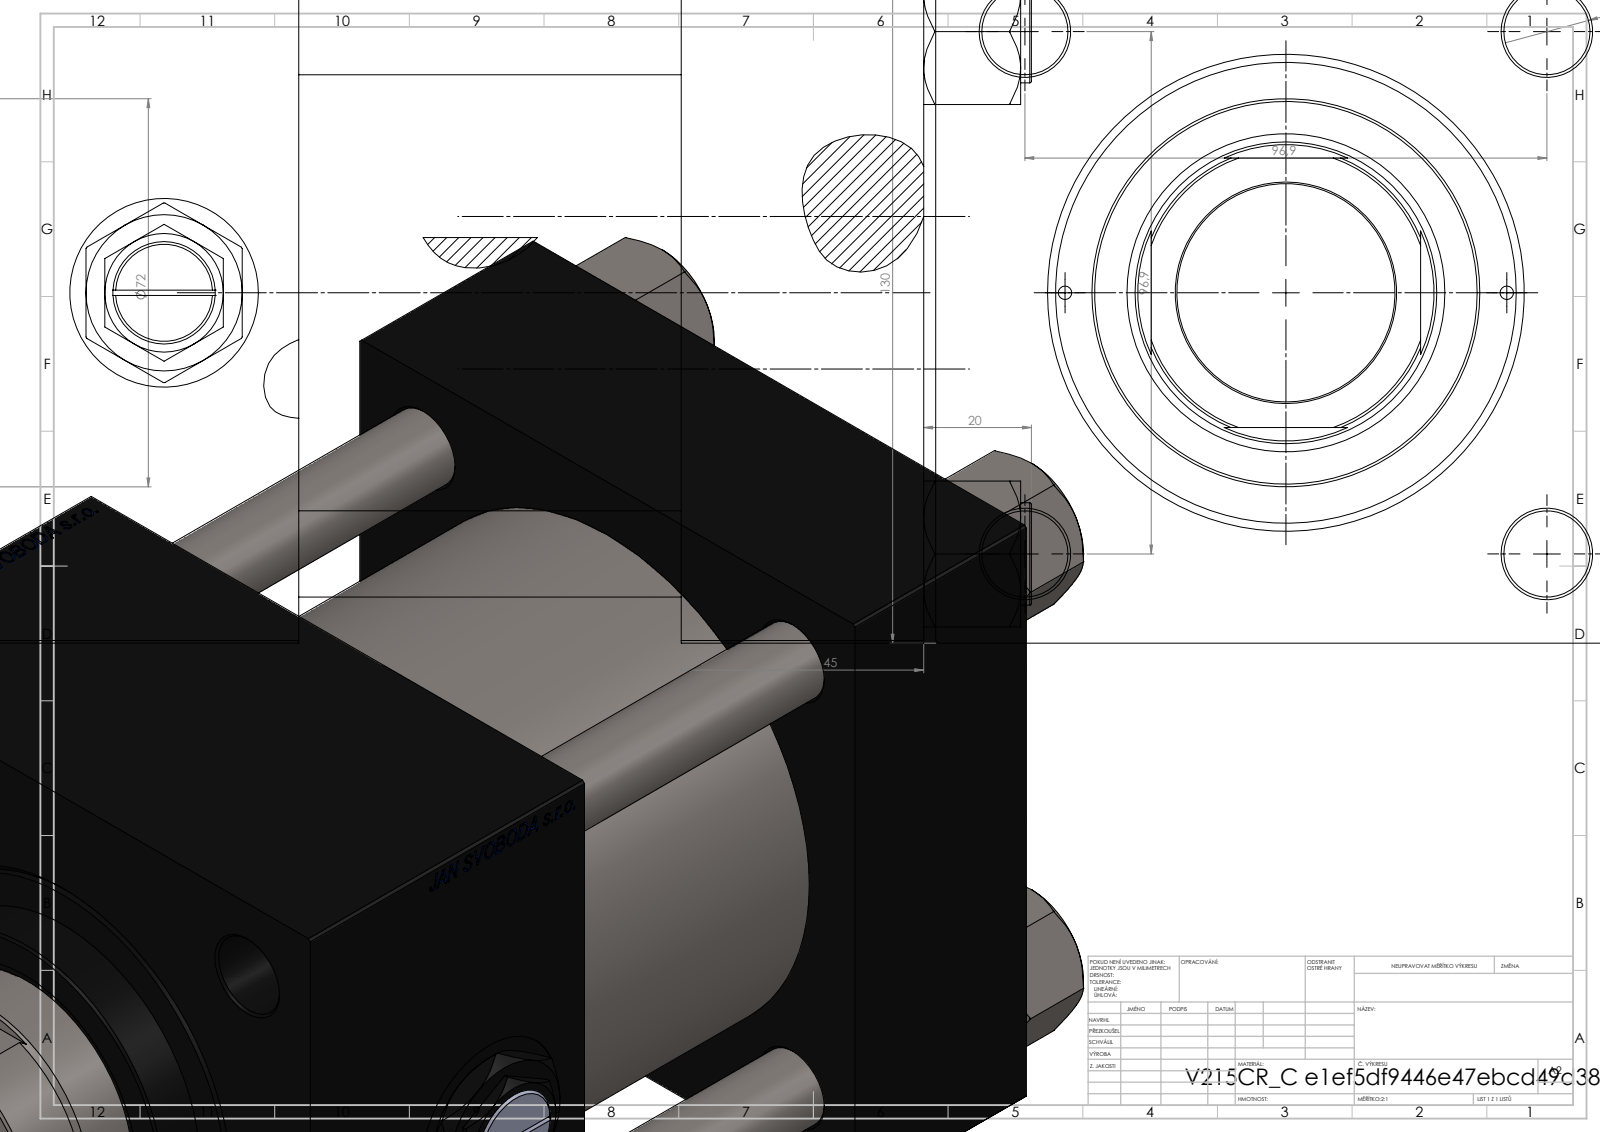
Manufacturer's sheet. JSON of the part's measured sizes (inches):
{"part_name": "V215CR_C_Body; Zatka_pro_OIL_PORT; NUT_M5_C; V215_VC_A (+2 more)", "step_written_by": "SolidWorks 2019 (CONFIG_CONTROL_DESIGN)", "units": "inches", "bodies": {"solids": 12, "faces": 1249, "planar": 599, "cylindrical": 94, "other": 556}, "overall_size": [9.567, 5.394, 5.118], "volume_in3": 150.4, "surface_area_in2": 521.9, "round_holes": [[0.63, 4], [0.098, 2], [0.276, 2], [1.041, 2], [1.378, 2], [1.594, 1], [2.205, 1], [2.323, 1], [2.992, 1], [3.366, 1], [3.937, 1]], "round_bosses_or_shafts": [[0.748, 4], [4.173, 1], [2.835, 1]], "partial_cylinders_radius": [[1.063, 1]], "face_to_face_distances": [5.118, 1.772, 7.402, 5.63, 4.567, 2.795, 2.835, 0.787, 2.008, 3.78], "hole_center_spacings": [1.93, 2.698, 3.815, 4.005, 1.614, 5.395, 3.228, 4.665]}
